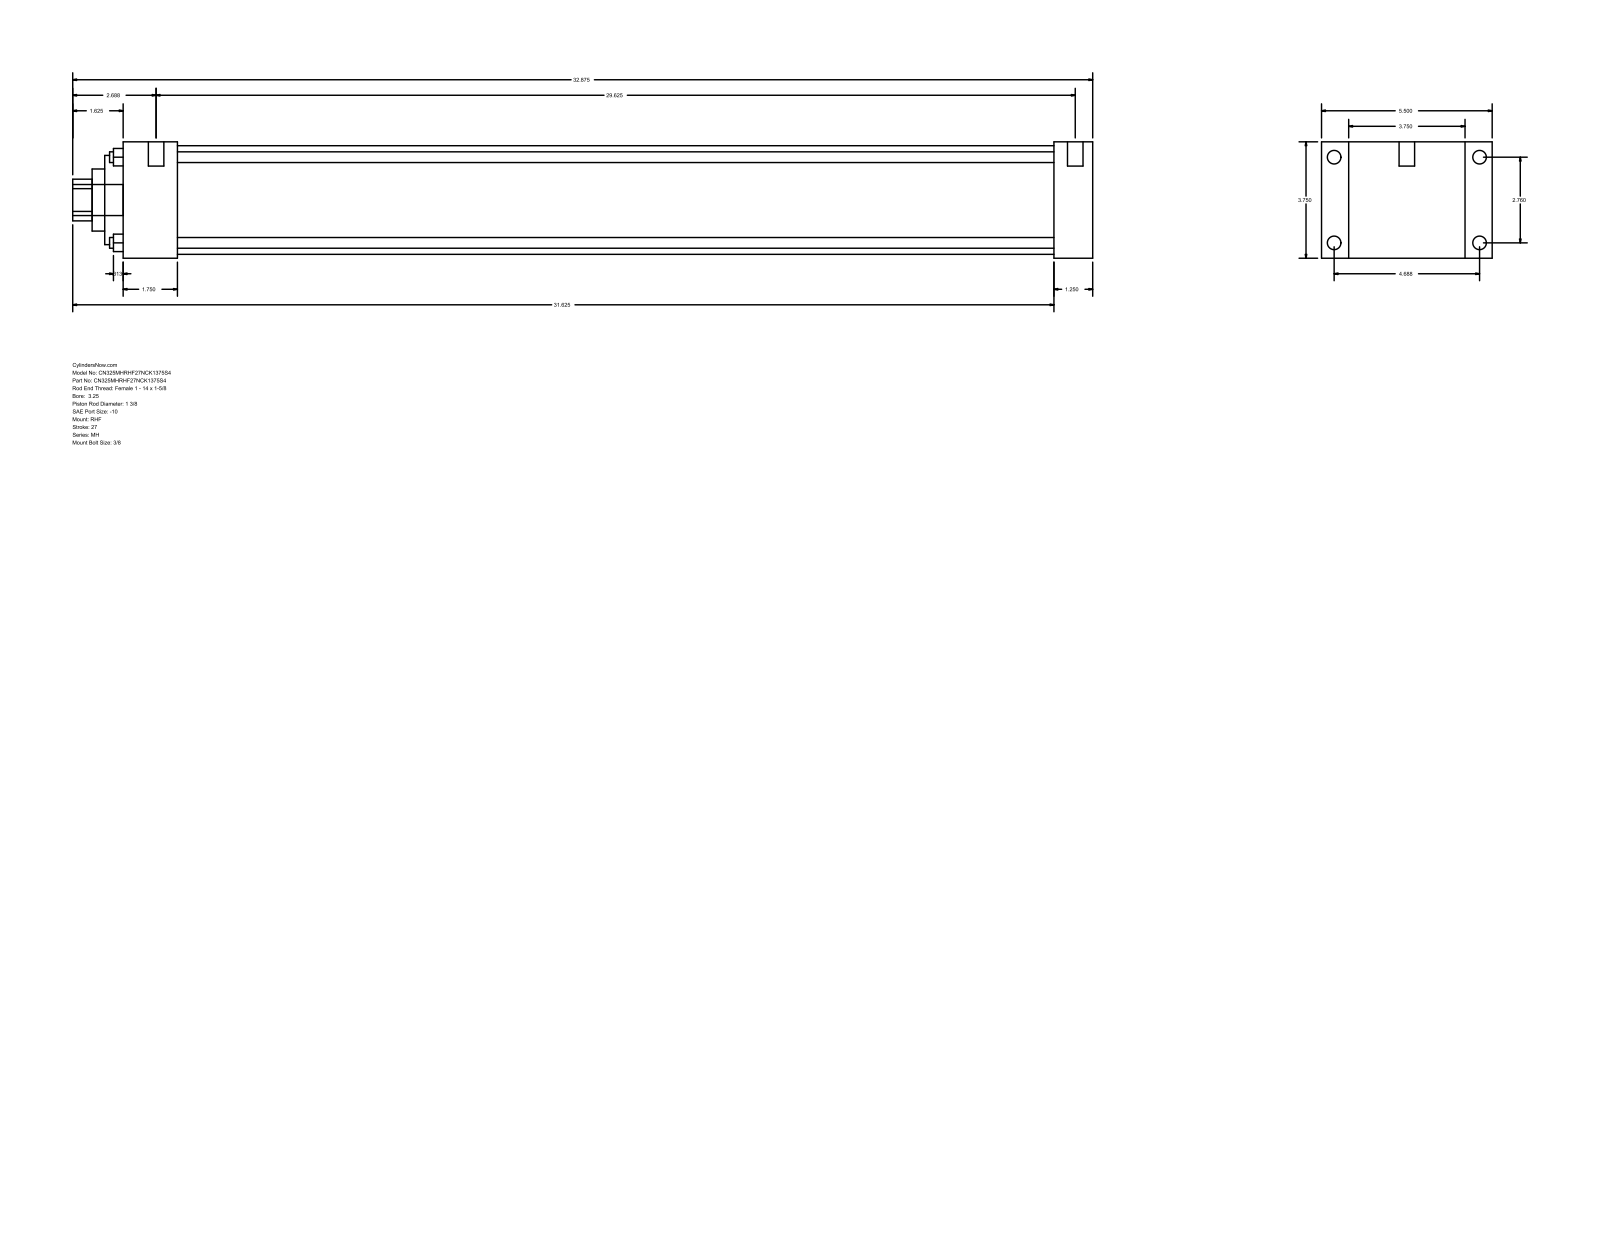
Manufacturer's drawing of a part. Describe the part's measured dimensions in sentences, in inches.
The part is named "MH_RHF__0325_1.375". Its 3-D file was written by "GSSL Pune (CONFIG_CONTROL_DESIGN)". It is 0 solids with 90 faces: 61 planar, 29 cylindrical and 0 other. Overall it measures 32.875 by 5.5 by 3.75 inches. Round holes: 4 of diameter 0.345, 1 of diameter 1.375, 1 of diameter 2, 1 of diameter 2.875, 1 of diameter 3.5. Round bosses or shafts: 4 of diameter 0.438, 4 of diameter 0.219, 2 of diameter 0.5, 1 of diameter 1. Partial cylindrical surfaces (rounded edges, fillets, slot ends): 1 of radius 0.672. The main face-to-face distances are 3.75, 1.25, 0.875, 4.625, 30, 31.25, 5.5, 1.75, 28.25, 29.5. The hole center spacings are 1.952, 2.76, 3.903.
